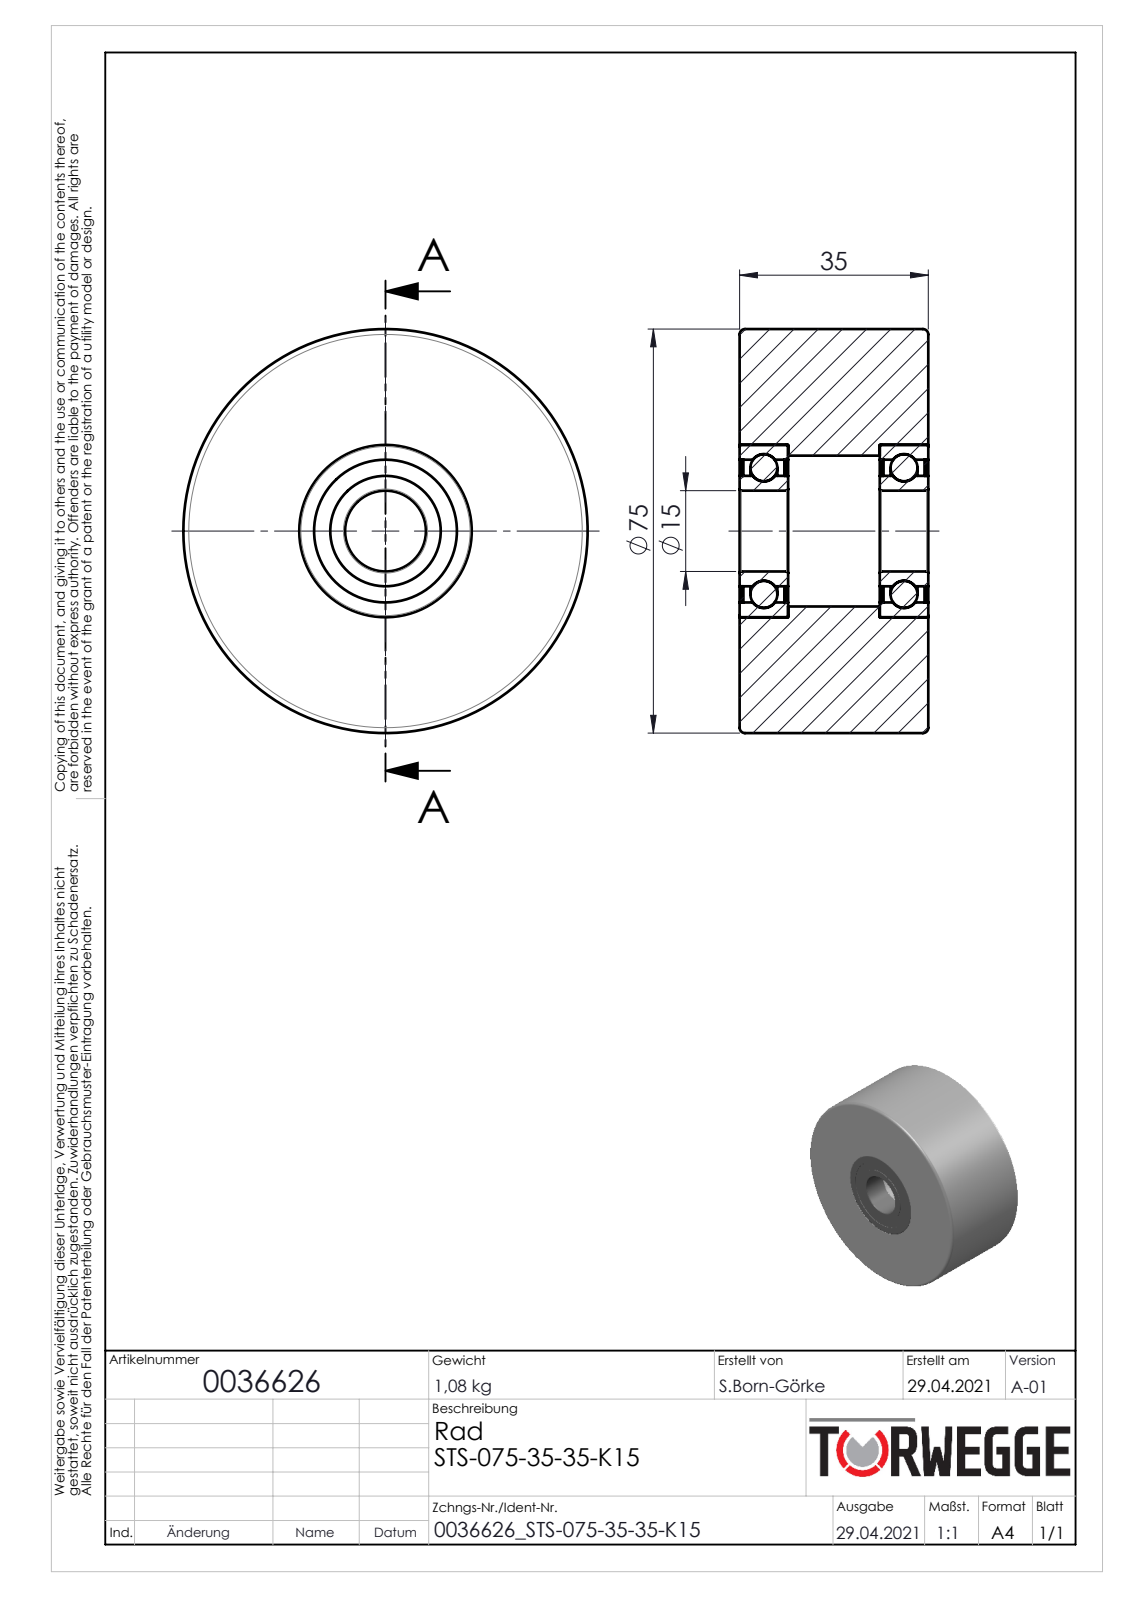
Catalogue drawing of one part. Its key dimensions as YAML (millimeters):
part_name: "0036626"
step_written_by: "SolidWorks 2020 (AUTOMOTIVE_DESIGN)"
units: millimeters
bodies: {solids: 11, faces: 108, planar: 20, cylindrical: 48, other: 40}
overall_size: [75, 75, 35]
volume: 139325
surface_area: 30404
round_holes:
  - {diameter: 15, count: 1}
  - {diameter: 20.5, count: 1}
  - {diameter: 26.5, count: 1}
  - {diameter: 28, count: 1}
  - {diameter: 32, count: 1}
round_bosses_or_shafts:
  - {diameter: 75, count: 1}
face_to_face_distances: [35, 26, 9, 0.7, 0.5, 8.3, 8.8, 8.1, 17, 34.3]
